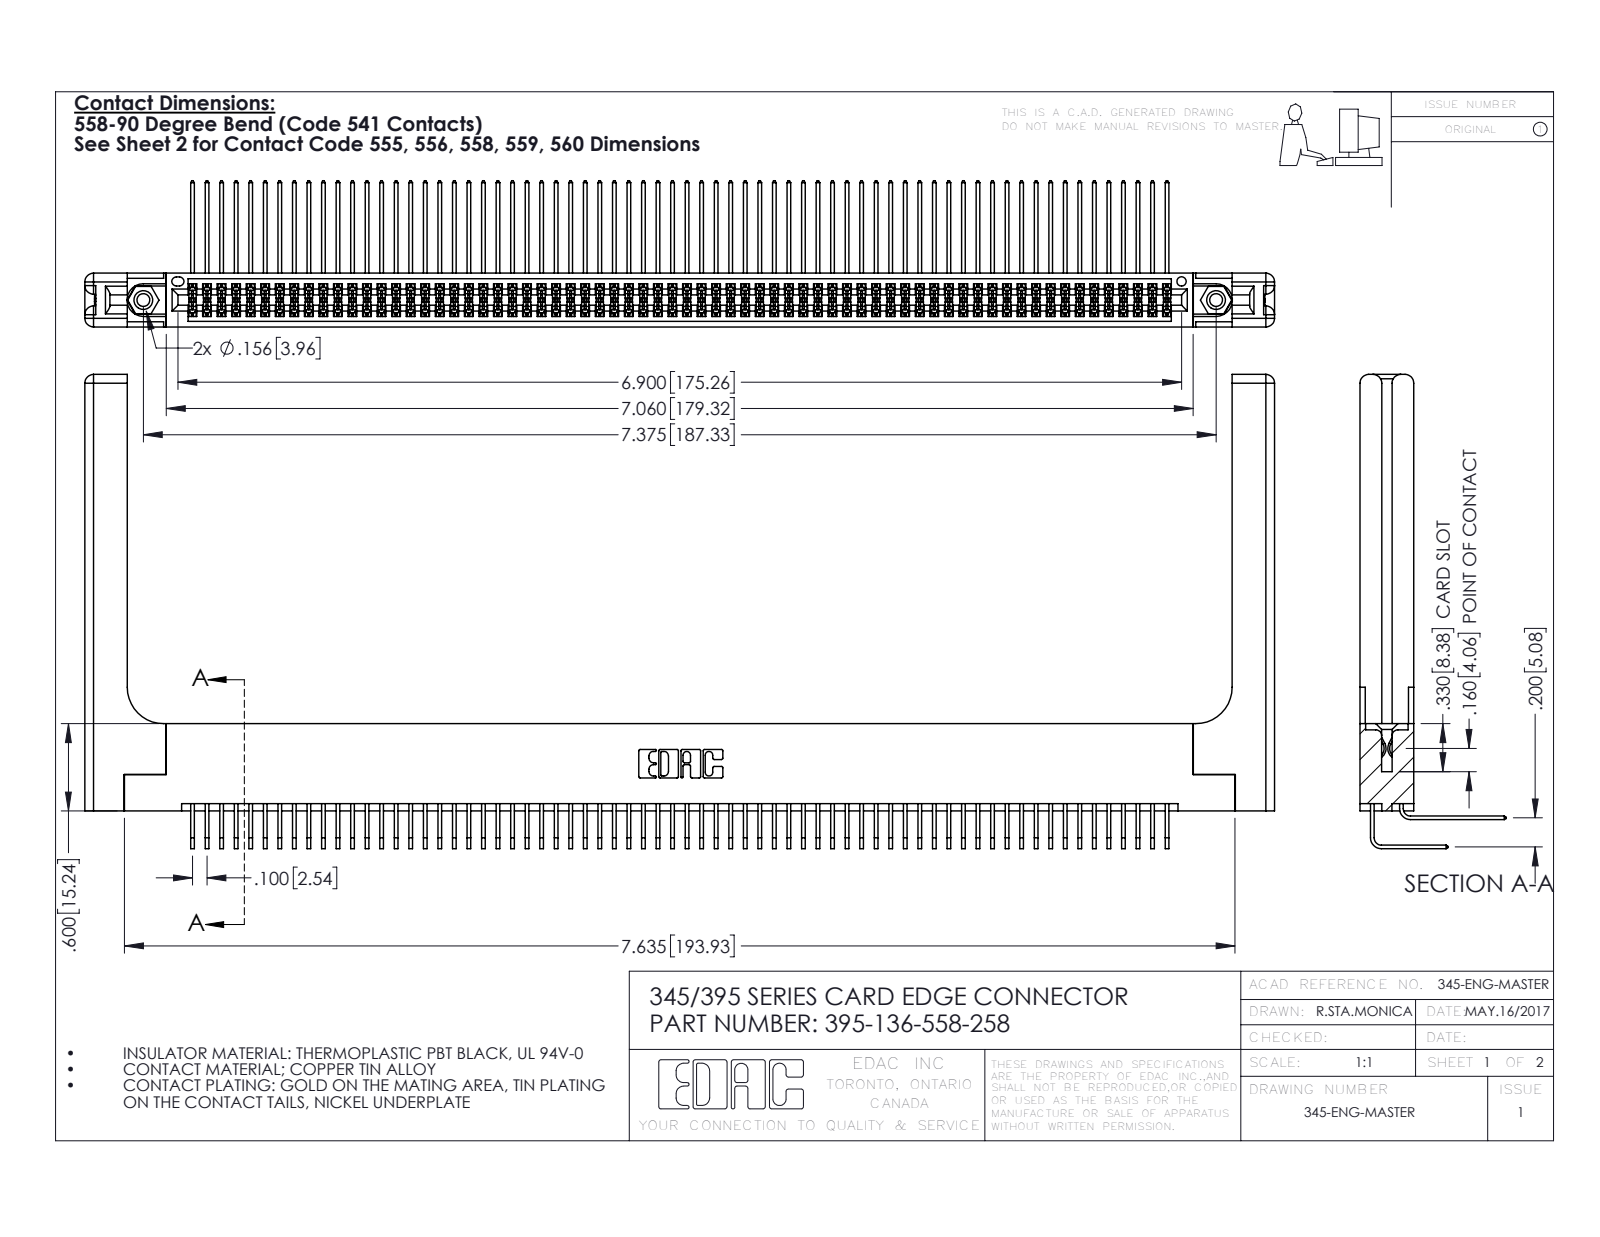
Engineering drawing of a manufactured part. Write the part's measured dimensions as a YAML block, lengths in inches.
part_name: "345 Part_Flush Mounting Lugs - 0.156 Dia-TH; 345-292-001_558 Tail - 2; 345-220-058_345-220-058; 395-136-558-258 (+2 more)"
step_written_by: "SolidWorks 2016 (CONFIG_CONTROL_DESIGN)"
units: inches
bodies: {solids: 141, faces: 7454, planar: 4988, cylindrical: 2406, other: 60}
overall_size: [8.179, 3.259, 1.005]
volume: 1.811
surface_area: 62.93
round_holes:
  - {diameter: 0.089, count: 2}
  - {diameter: 0.125, count: 2}
  - {diameter: 0.156, count: 2}
  - {diameter: 0.064, count: 1}
round_bosses_or_shafts:
  - {diameter: 0.155, count: 2}
partial_cylinders:
  - {radius: 0.006, count: 271}
  - {radius: 0.01, count: 22}
  - {radius: 0.06, count: 16}
  - {radius: 0.007, count: 6}
  - {radius: 0.031, count: 6}
  - {radius: 0.026, count: 3}
  - {radius: 0.014, count: 2}
  - {radius: 0.019, count: 2}
face_to_face_distances: [0.072, 0.298, 0.2, 0.37, 0.098, 0.272, 0.025, 0.225, 0.025, 0.175]
hole_center_spacings: [0.27, 7.139, 7.375]
